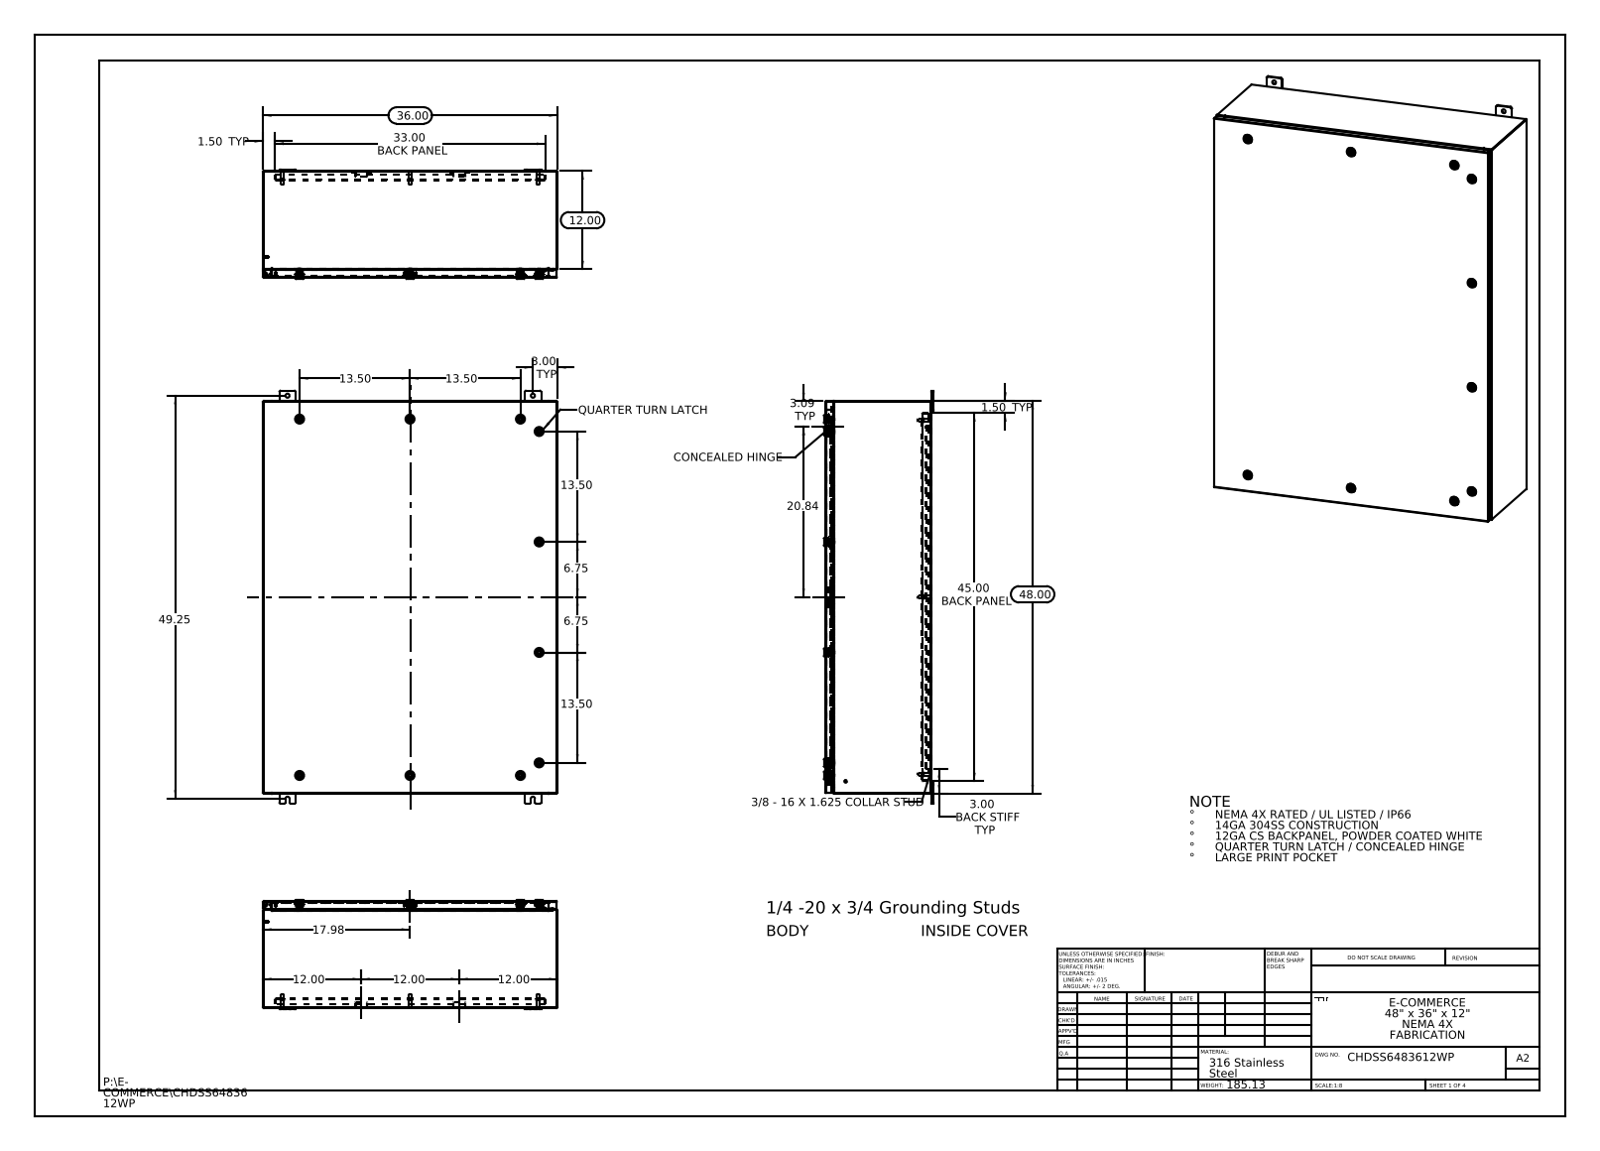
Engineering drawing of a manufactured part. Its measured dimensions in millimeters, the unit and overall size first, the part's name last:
Units: millimetres
Overall size (bounding box): 1282.7 × 914.4 × 339.2
Round holes (diameter × count): ⌀12.7 ×12, ⌀5 ×10, ⌀10 ×10, ⌀10.2 ×10, ⌀16 ×10, ⌀20 ×10, ⌀3.5 ×6, ⌀6.4 ×6, ⌀5.4 ×1
Round bosses / shafts (diameter × count): ⌀6 ×12, ⌀28 ×10, ⌀19.8 ×10, ⌀15.9 ×10, ⌀15.5 ×10, ⌀13.5 ×10, ⌀10 ×10, ⌀2.9 ×10
Partial cylindrical surfaces — rounded edges, fillets, slot ends (radius × count): R0.2 ×330, R3 ×330, R0.7 ×120, R0.5 ×40, R5 ×40, R0.3 ×34, R2.2 ×30, R4.8 ×24
Main face-to-face distances: 1.9, 1.9, 326.7, 328.6, 330.5, 328.5, 2.6, 25.4, 27.3, 301.3
Hole centre spacings: 342.9, 508, 511.1, 549.3, 685.8, 965.3, 1158.1, 1168
Volume: 10 710 000 mm³ · Surface area: 10 480 000 mm²
Bodies: 94 solids, 9060 faces (2626 planar, 2826 cylindrical, 3608 other)
Part name (STEP PRODUCT): CHDSS6483612WP; CHDSS6483612WP Body; CHDSS6483612WP Mounting Feet; Screw-221320-IB-Industrilas_Screw-221320-IB-Industrilas (+8 more)
STEP written by: SolidWorks 2013 (CONFIG_CONTROL_DESIGN)
